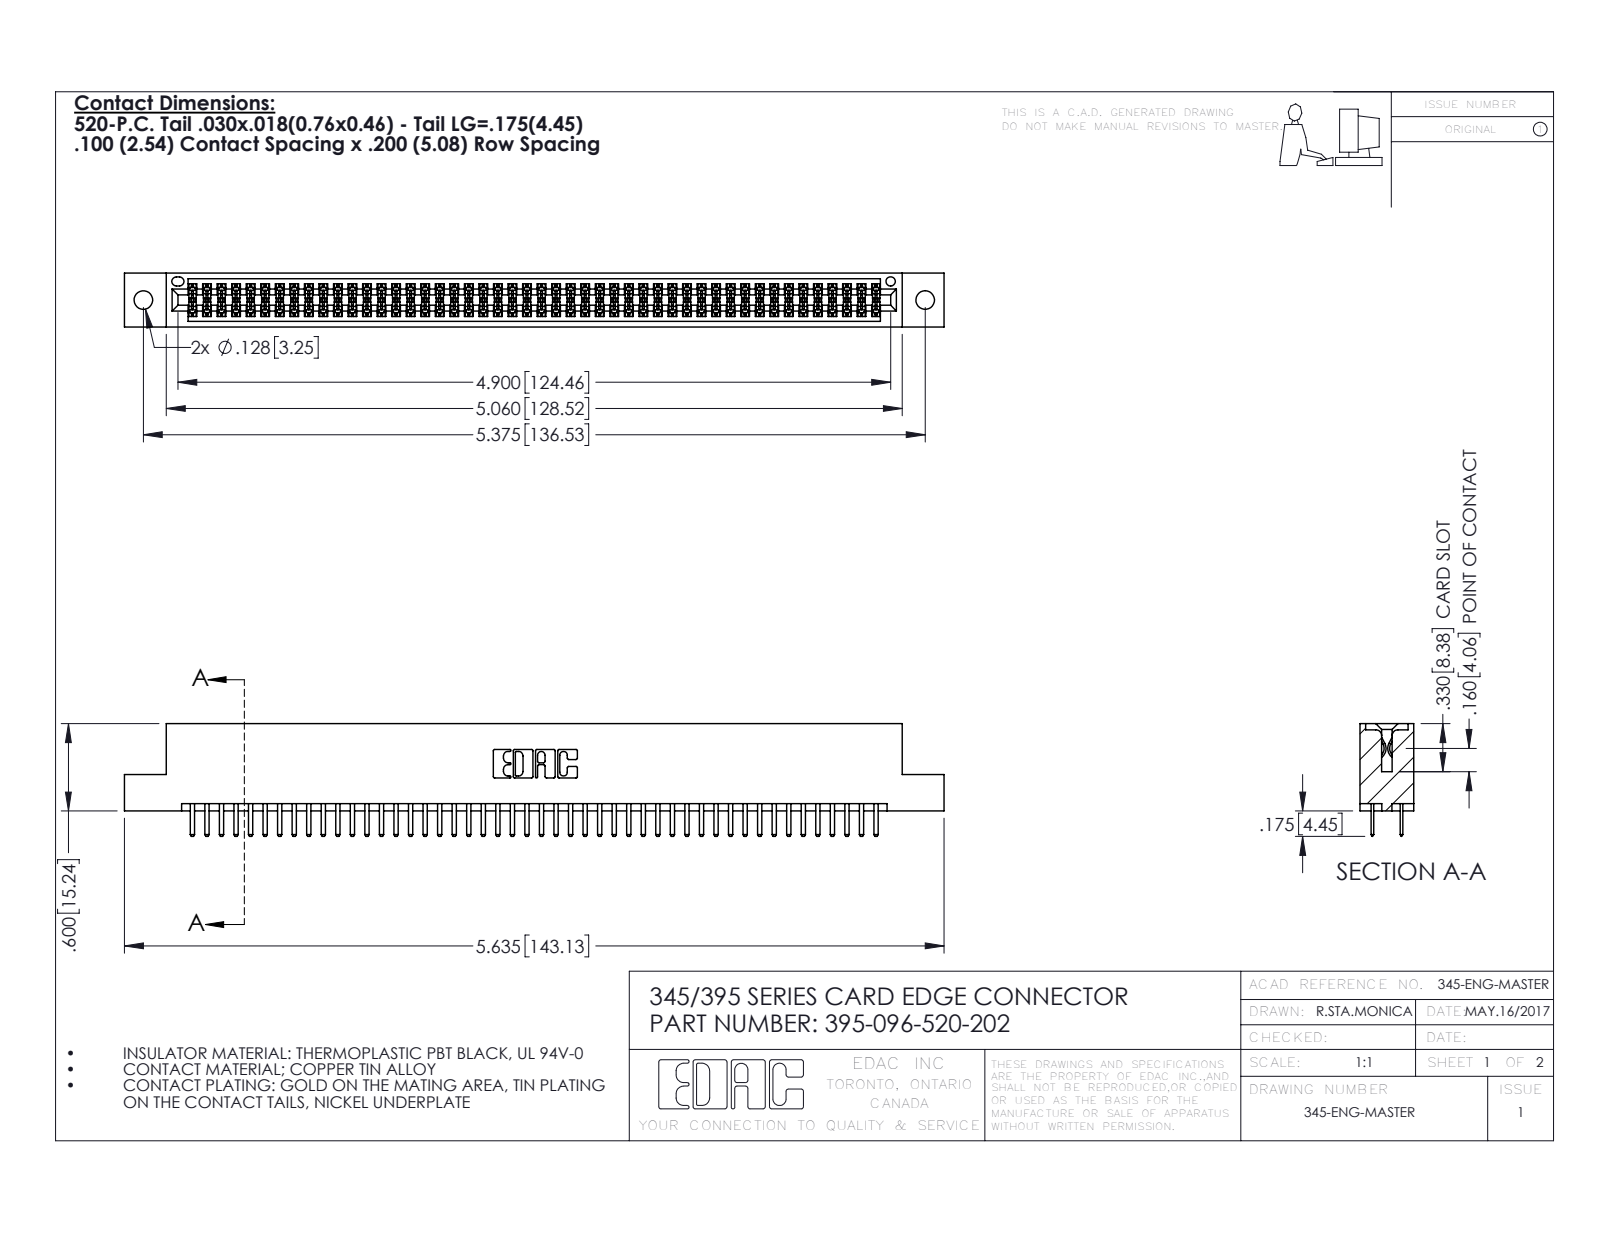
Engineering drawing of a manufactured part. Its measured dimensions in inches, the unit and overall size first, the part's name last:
Units: inches
Overall size (bounding box): 5.635 × 0.775 × 0.37
Round holes (diameter × count): ⌀0.128 ×2, ⌀0.064 ×1
Partial cylindrical surfaces — rounded edges, fillets, slot ends (radius × count): R0.006 ×144, R0.01 ×100, R0.01 ×22, R0.007 ×6, R0.031 ×6, R0.026 ×3, R0.014 ×2, R0.019 ×2
Main face-to-face distances: 0.298, 0.072, 0.2, 0.37, 0.098, 0.272, 0.025, 0.225, 0.022, 0.072
Hole centre spacings: 0.27, 5.139, 5.375
Volume: 0.847 in³ · Surface area: 31.42 in²
Bodies: 97 solids, 5310 faces (3440 planar, 1870 cylindrical, 0 other)
Part name (STEP PRODUCT): 345 Part_Flush Mounting Lugs - 0.128 Dia; 395-096-520-202; 345-292-001_345-293-120
STEP written by: SolidWorks 2016 (CONFIG_CONTROL_DESIGN)
